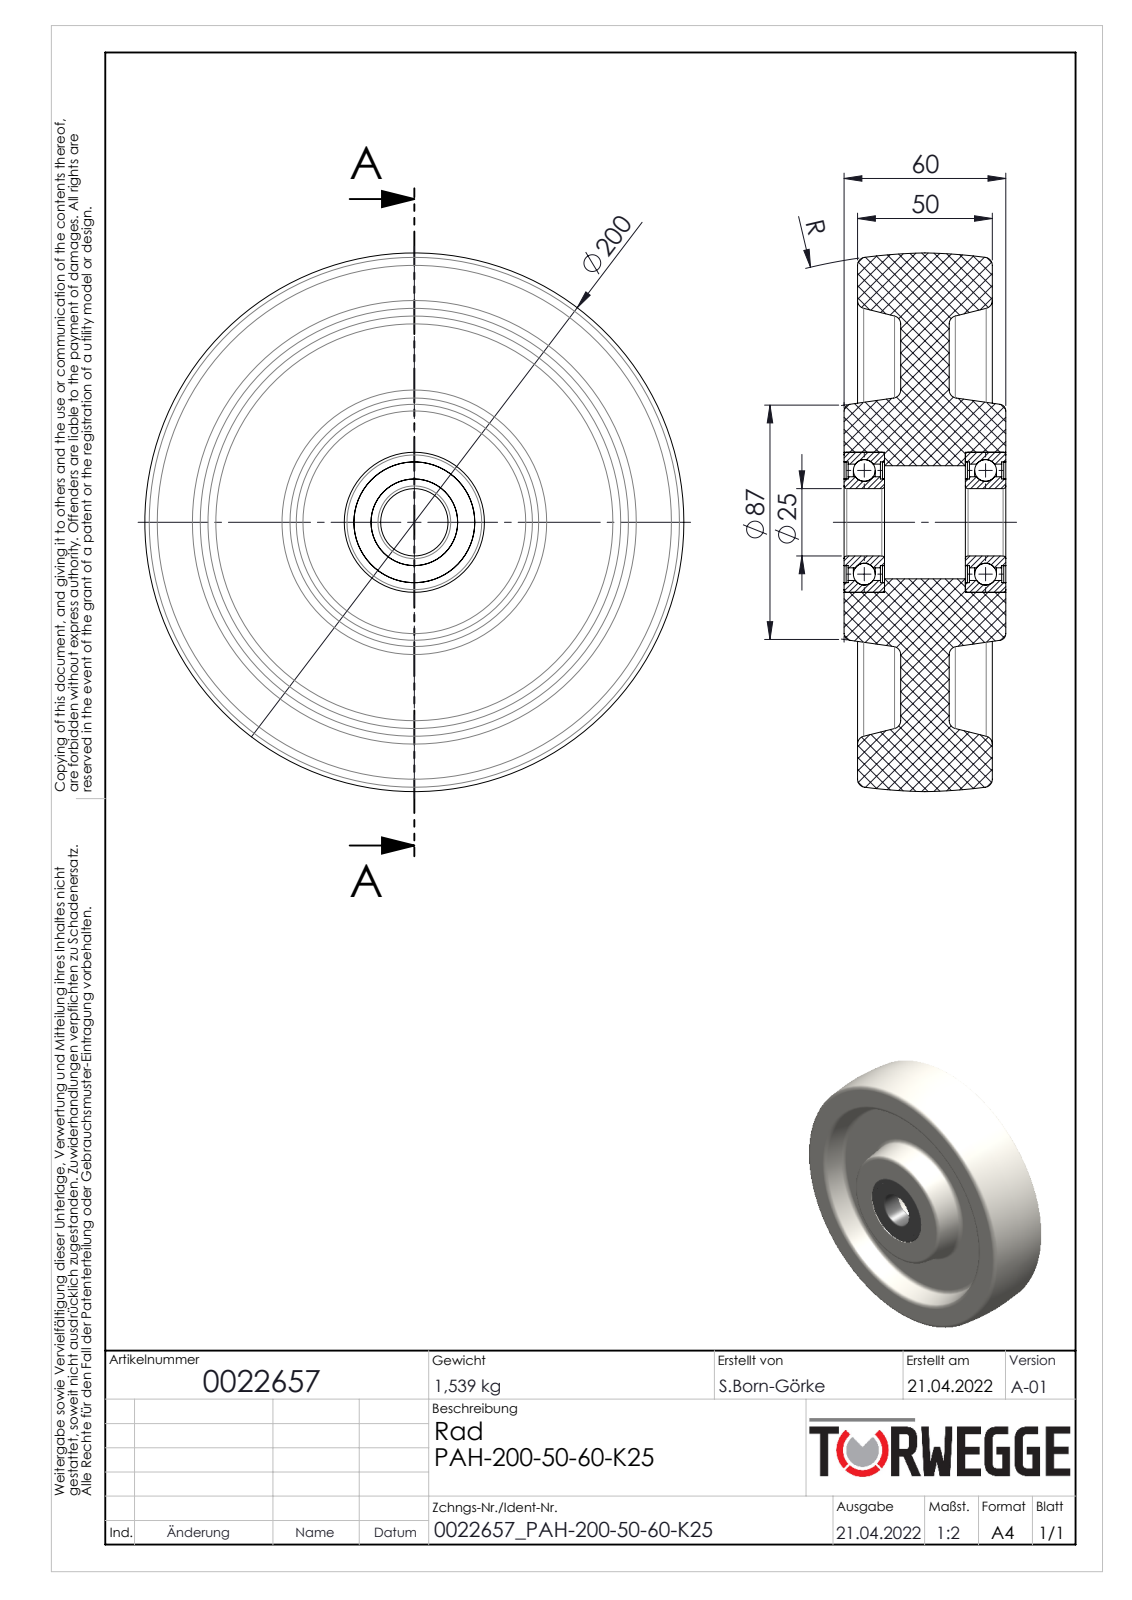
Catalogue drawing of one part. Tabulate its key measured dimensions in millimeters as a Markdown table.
| quantity | value |
| --- | --- |
| part name | 0022657 |
| STEP written by | SolidWorks 2020 (AUTOMOTIVE_DESIGN) |
| units | millimeters |
| bodies | 11 solids, 162 faces (32 planar, 62 cylindrical, 68 other) |
| overall size | 200 × 200 × 60 |
| volume | 1 138 000 mm³ |
| surface area | 148 715 mm² |
| round holes (diameter × count) | 25 × 1, 32.16 × 1, 42 × 1, 43.2 × 1, 44.85 × 1, 52 × 1 |
| round bosses / shafts (diameter × count) | 33.8 × 1 |
| main face-to-face distances | 16, 34, 18, 5, 21, 39, 55, 50, 45, 60 |
